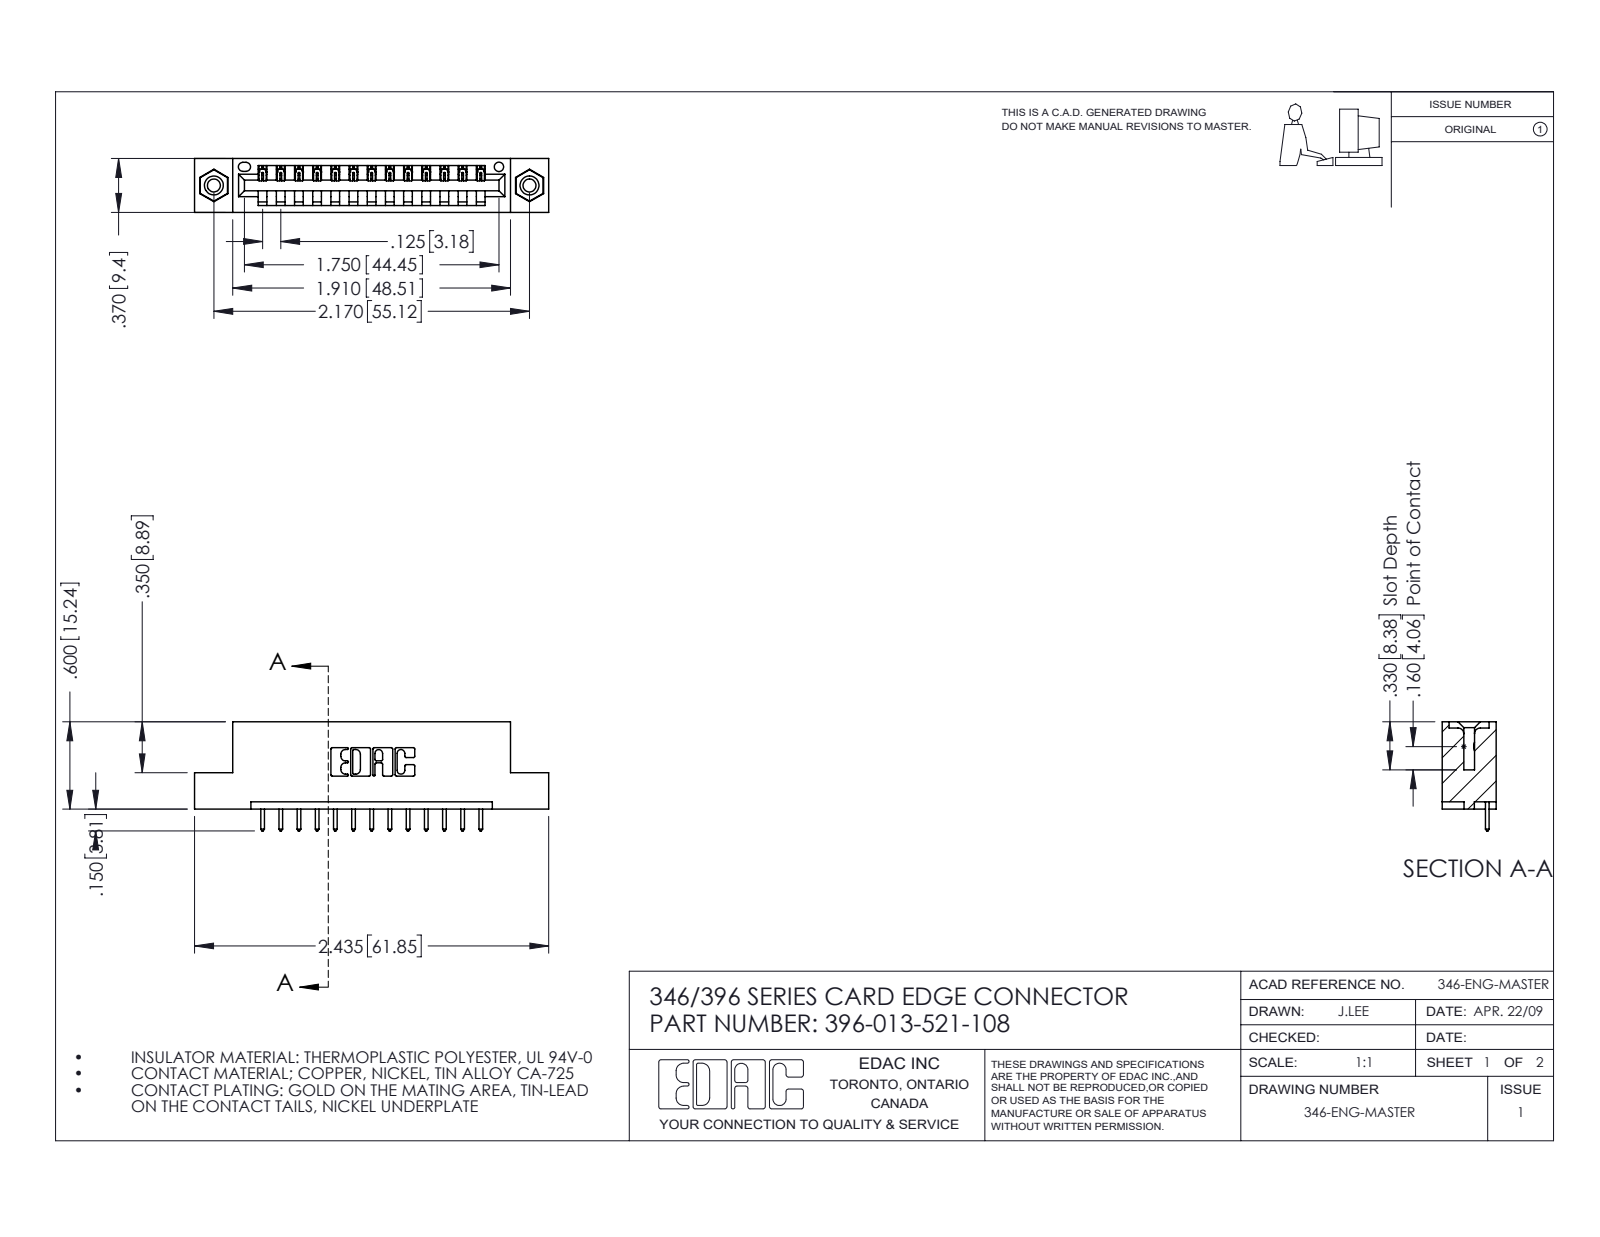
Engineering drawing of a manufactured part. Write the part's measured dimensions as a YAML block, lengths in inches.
part_name: "345-250-001_345-250-003-102; 396-013-521-108; 345-292-001_345-293-121; 346 Part_Flush Mounting Lugs - 0.156 Dia-TI"
step_written_by: "SolidWorks 2016 (CONFIG_CONTROL_DESIGN)"
units: inches
bodies: {solids: 16, faces: 936, planar: 628, cylindrical: 292, other: 16}
overall_size: [2.435, 0.75, 0.37]
volume: 0.346
surface_area: 10.32
round_holes:
  - {diameter: 0.089, count: 2}
  - {diameter: 0.125, count: 2}
  - {diameter: 0.156, count: 2}
  - {diameter: 0.064, count: 1}
round_bosses_or_shafts:
  - {diameter: 0.155, count: 2}
partial_cylinders:
  - {radius: 0.006, count: 26}
  - {radius: 0.01, count: 26}
  - {radius: 0.01, count: 22}
  - {radius: 0.007, count: 6}
  - {radius: 0.031, count: 6}
  - {radius: 0.026, count: 3}
  - {radius: 0.031, count: 2}
  - {radius: 0.04, count: 2}
face_to_face_distances: [0.25, 0.048, 0.322, 0.37, 0.072, 0.298, 0.025, 0.148, 0.222, 0.1]
hole_center_spacings: [0.246, 1.964, 2.17]
